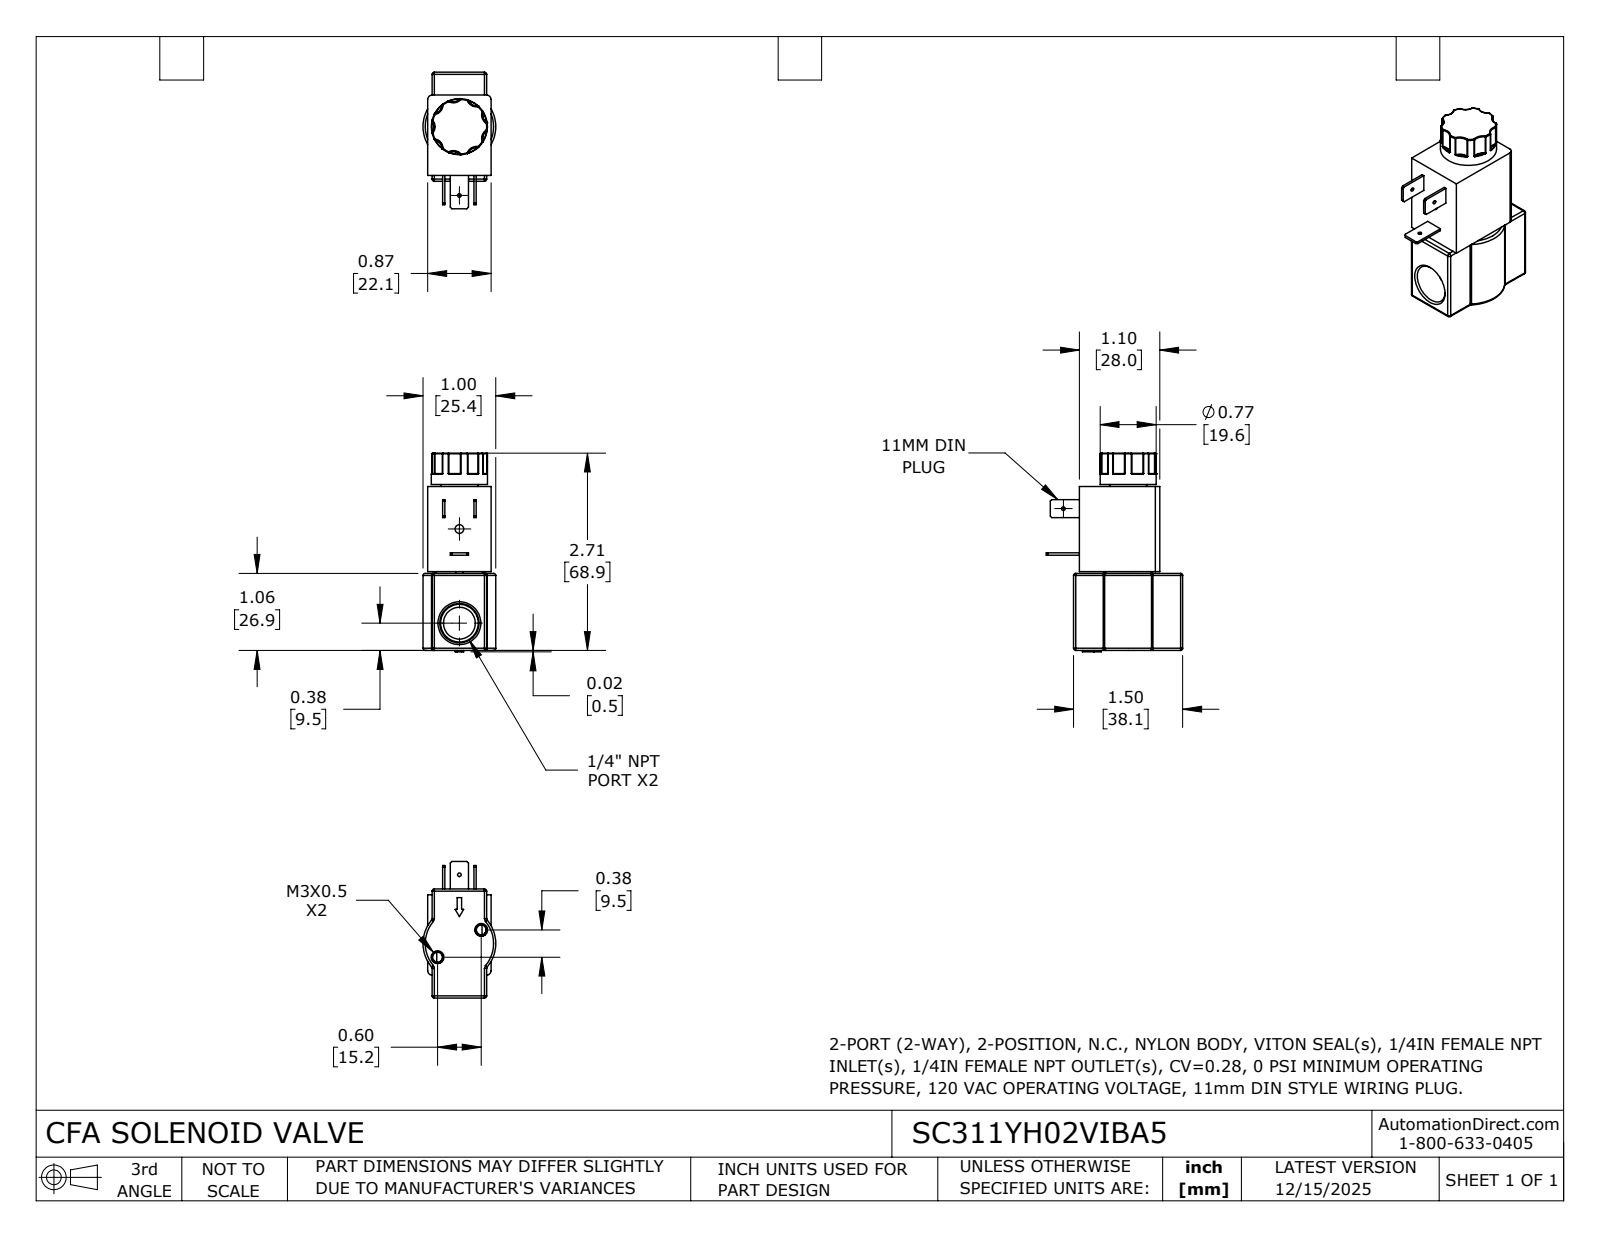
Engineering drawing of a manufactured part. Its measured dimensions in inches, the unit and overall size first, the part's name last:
Units: inches
Overall size (bounding box): 2.732 × 1.877 × 1
Round holes (diameter × count): ⌀0.05 ×2, ⌀0.136 ×2, ⌀0.12 ×1, ⌀0.438 ×1
Round bosses / shafts (diameter × count): ⌀0.77 ×1
Partial cylindrical surfaces — rounded edges, fillets, slot ends (radius × count): R0.01 ×18, R0.03 ×16, R0.133 ×7, R0.06 ×2, R0.132 ×2, R0.295 ×2, R0.311 ×1, R0.5 ×1
Main face-to-face distances: 0.06, 0.81, 0.87, 1.104, 2.252, 1.06, 1.192, 0.75, 1.085, 0.025
Hole centre spacings: 0.707, 0.815, 1.172, 1.293
Volume: 2.397 in³ · Surface area: 17.71 in²
Bodies: 1 solid, 383 faces (62 planar, 117 cylindrical, 204 other)
Part name (STEP PRODUCT): SC311YH02VIBA5
STEP written by: SolidWorks 2024 (CONFIG_CONTROL_DESIGN)
